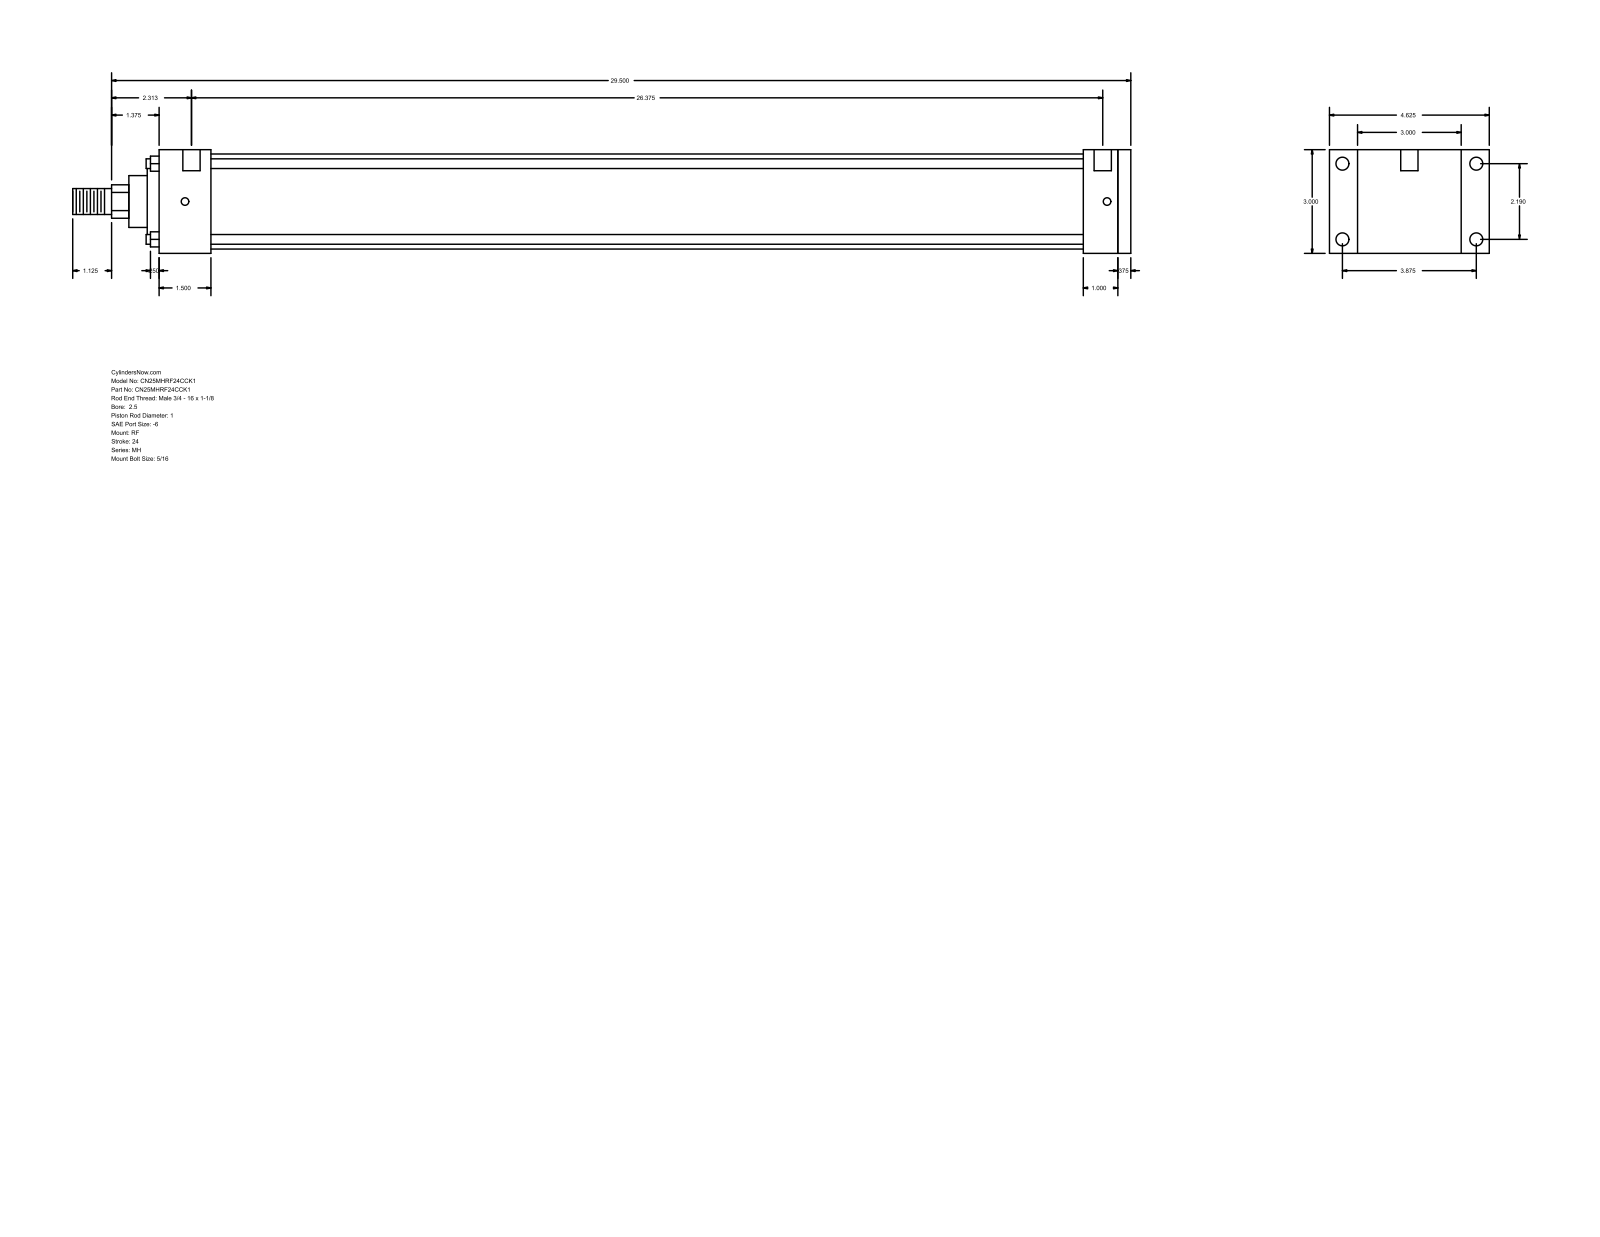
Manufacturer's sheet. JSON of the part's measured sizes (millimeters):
{"part_name": "MH_RF__0250_1", "step_written_by": "GSSL Pune (CONFIG_CONTROL_DESIGN)", "units": "millimeters", "bodies": {"solids": 0, "faces": 94, "planar": 65, "cylindrical": 29, "other": 0}, "overall_size": [777.88, 117.47, 76.2], "round_holes": [[5.56, 4], [9.53, 4], [12.7, 2]], "round_bosses_or_shafts": [[7.14, 4], [69.85, 1], [60.33, 1], [38.1, 1], [25.4, 1], [19.05, 1]], "partial_cylinders_radius": [[12.29, 1]], "face_to_face_distances": [76.2, 9.53, 714.38, 704.85, 34.92, 25.39, 679.46, 38.11, 641.35, 666.74], "hole_center_spacings": [55.62, 98.42, 113.05, 677.86, 3.18, 4.76, 669.92, 673.1]}
